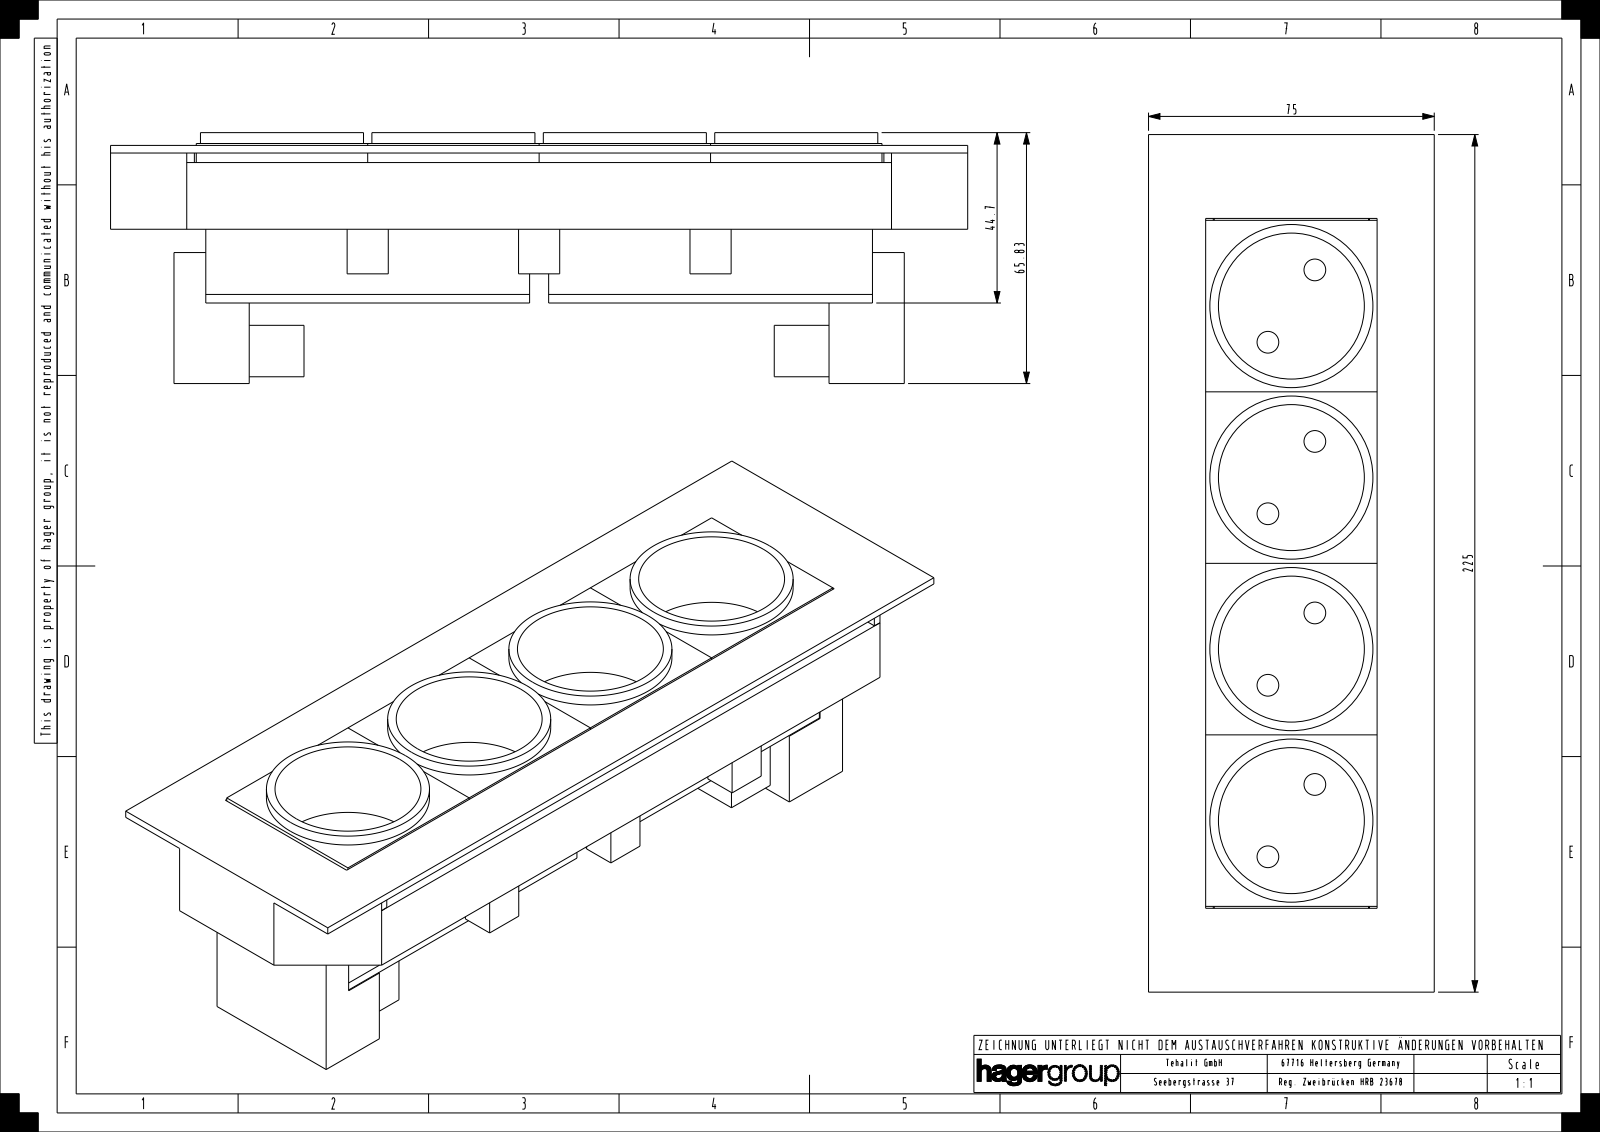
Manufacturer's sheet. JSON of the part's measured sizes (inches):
{"part_name": "T-02341_1; W4G0443_00_1; W1C0438_00_1; W1D1115_00_1 (+8 more)", "step_written_by": "CREO PARAMETRIC BY PTC INC, 2022281 (AUTOMOTIVE_DESIGN)", "units": "inches", "bodies": {"solids": 92, "faces": 53922, "planar": 22950, "cylindrical": 17876, "other": 13096}, "overall_size": [9.202, 2.953, 2.595], "volume_in3": 11.03, "surface_area_in2": 566.6, "round_holes": [[0.102, 16], [0.055, 12], [0.071, 12], [0.118, 12], [0.098, 10], [0.079, 6], [0.02, 4], [0.094, 4], [0.222, 4], [0.226, 4], [0.327, 4], [0.177, 3]], "round_bosses_or_shafts": [[0.071, 48], [0.087, 12], [0.046, 10], [0.118, 7], [0.138, 6], [1.512, 4], [0.114, 4], [0.031, 4]], "partial_cylinders_radius": [[0.008, 6494], [0.012, 1350], [0.02, 1087], [0.006, 670], [0.004, 662], [0.039, 441], [0.01, 159], [0.024, 134]], "face_to_face_distances": [0.071, 0.88, 0.038, 0.951, 0.63, 0.927, 1.772, 0.559, 1.51, 0.035], "hole_center_spacings": [1.772, 0.494, 0.507, 0.519, 0.65, 1.044, 0.601, 0.889]}
